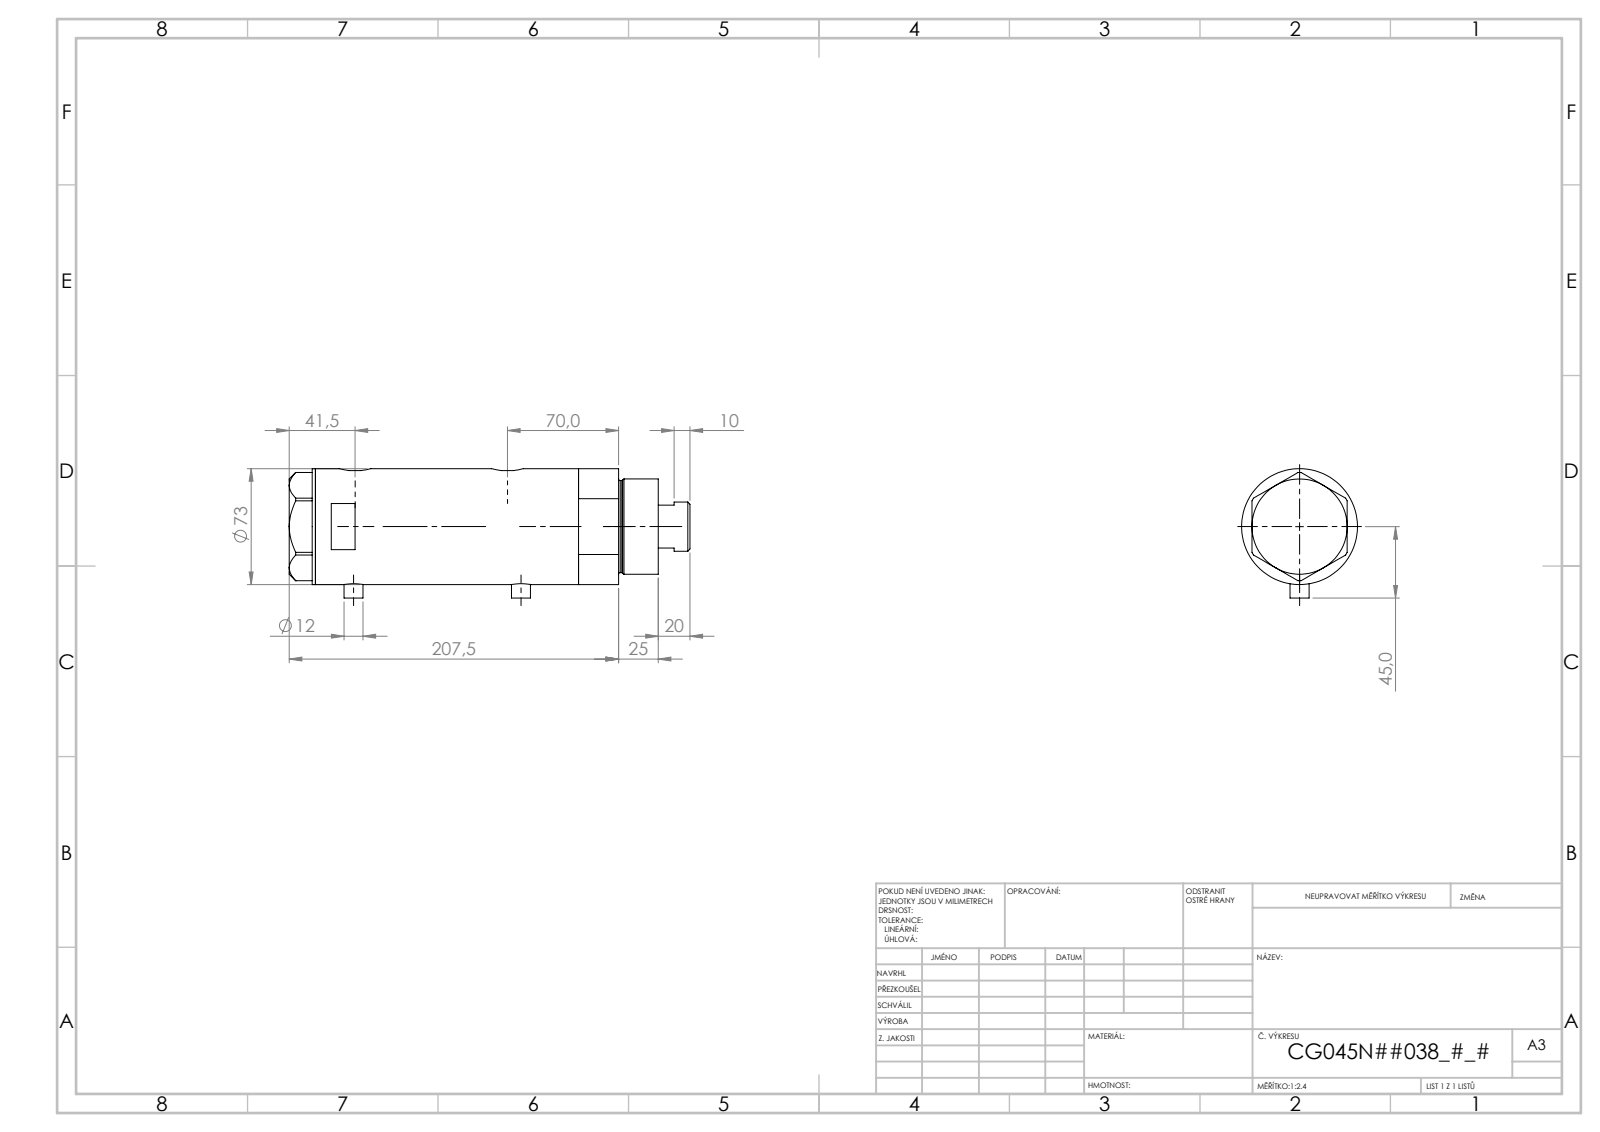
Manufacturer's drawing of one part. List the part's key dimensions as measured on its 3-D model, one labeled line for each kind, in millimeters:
Part name (STEP PRODUCT): V270CG_BACK; V270CG_FRONT; V270CG_VC; V270CG_MIDDLE
STEP written by: SolidWorks 2019 (CONFIG_CONTROL_DESIGN)
Units: millimetres
Bodies: 4 solids, 125 faces (50 planar, 55 cylindrical, 20 other)
Overall size (bounding box): 229.52 × 74.1 × 73
Volume: 795 925 mm³ · Surface area: 137 847 mm²
Round holes (diameter × count): ⌀5 ×2, ⌀12.5 ×2, ⌀13.16 ×2, ⌀10.5 ×1, ⌀32 ×1, ⌀33.5 ×1, ⌀45 ×1, ⌀48 ×1, ⌀64 ×1
Round bosses / shafts (diameter × count): ⌀12 ×2, ⌀73 ×1, ⌀60 ×1, ⌀58 ×1, ⌀31 ×1
Partial cylindrical surfaces — rounded edges, fillets, slot ends (radius × count): R10 ×2
Main face-to-face distances: 105.15, 42.5, 121.65, 79.15, 16.5, 16.51, 26, 25.99, 105.14, 193.02
Hole centre spacings: 89.65, 0.99, 1, 8.5, 8.51, 80.15, 81.14, 81.15
